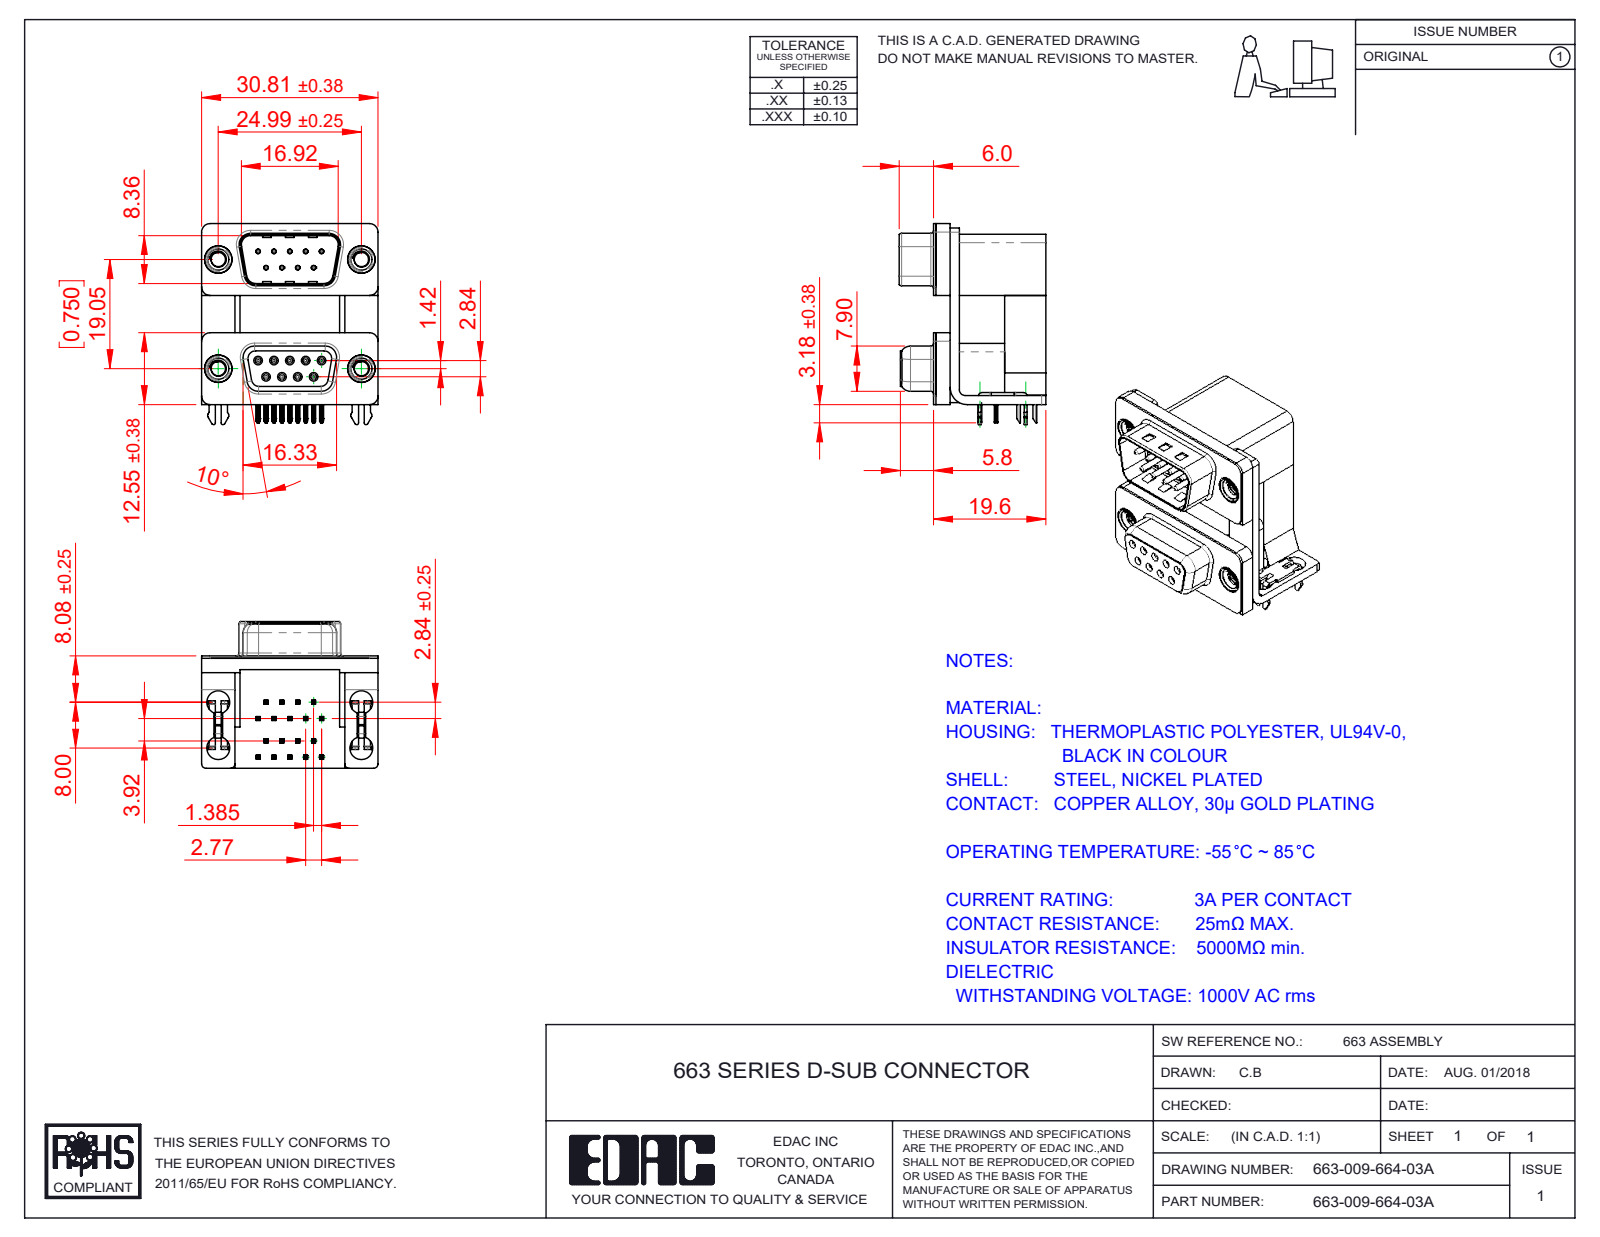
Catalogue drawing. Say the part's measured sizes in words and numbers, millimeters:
The part is named "663 Contact Bottom Upper_M; 663 Housing Upper_09 Contacts M; 663 Shell Receptacle_09 Contacts; 663 Mounting Bracket_2ProngM (+8 more)". Its 3-D file was written by "SolidWorks 2020 (CONFIG_CONTROL_DESIGN)". It is 31 solids with 2685 faces: 1365 planar, 753 cylindrical and 567 other. Overall it measures 35.1 by 30.81 by 25.6 millimeters. Its volume is 10 810 cubic millimeters and its surface area 12 747 square millimeters. Round holes: 18 of diameter 0.8, 9 of diameter 0.35, 9 of diameter 0.9, 8 of diameter 4, 4 of diameter 2.5, 4 of diameter 3.5, 4 of diameter 4.8, 4 of diameter 5. Round bosses or shafts: 9 of diameter 1.2, 9 of diameter 0.75, 4 of diameter 4.9, 4 of diameter 4.75, 4 of diameter 3.9. Partial cylindrical surfaces (rounded edges, fillets, slot ends): 74 of radius 0.1, 46 of radius 0.25, 36 of radius 0.15, 18 of radius 0.12, 18 of radius 0.35, 16 of radius 0.5, 15 of radius 1.5, 10 of radius 0.75. The main face-to-face distances are 0.4, 2.5, 16.7, 19.2, 9.5, 7.2, 12, 1.6, 19.6, 12.4. The hole center spacings are 3.16, 2.77, 19.25, 19.05, 5.54, 19.84, 16.27, 21.93.
